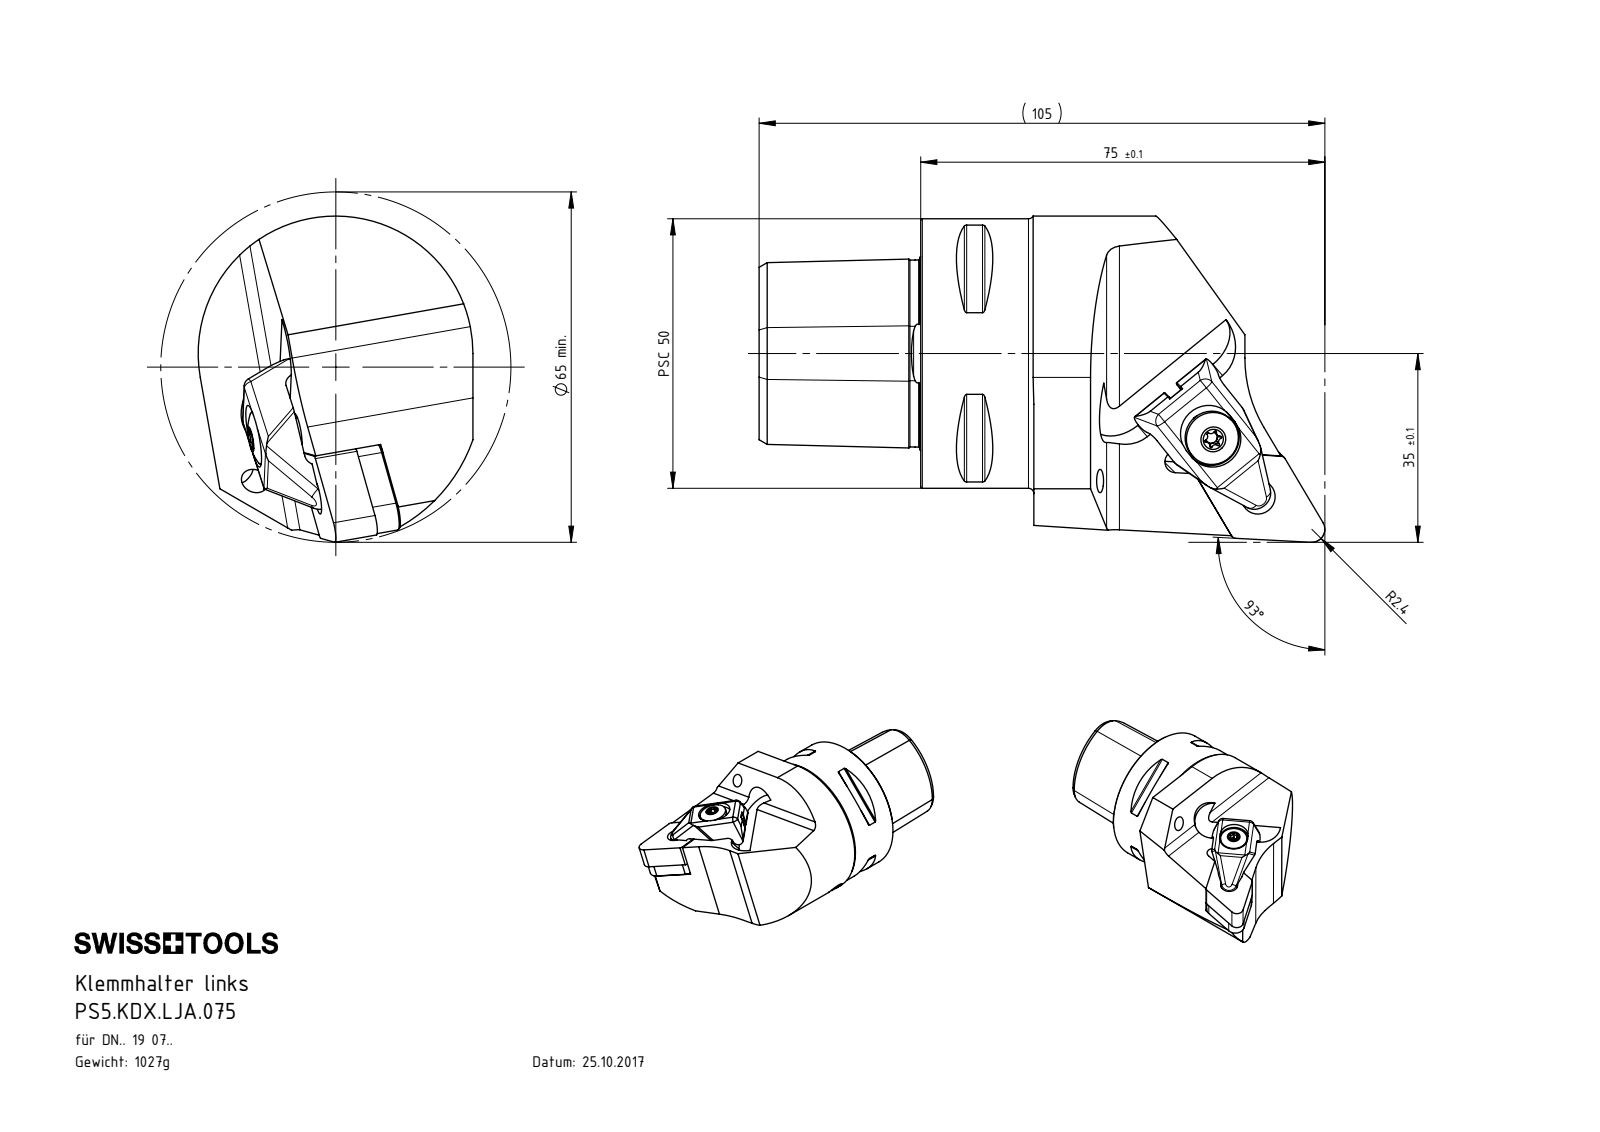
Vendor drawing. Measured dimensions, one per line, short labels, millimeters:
name: DNMG190724; Feder; Bratze komplett; Spannschraube (+6 more)
written by: SolidWorks 2017 (CONFIG_CONTROL_DESIGN)
unit: mm
bodies: 9 solids, 410 faces (106 planar, 145 cylindrical, 159 other)
size: 105.07 × 60.57 × 51
volume: 129 904 mm³; area: 27 478 mm²
holes: 3× ⌀5, 2× ⌀4.2, 1× ⌀4, 1× ⌀5.75, 1× ⌀6, 1× ⌀6.1, 1× ⌀6.35, 1× ⌀8.15, 1× ⌀8.5, 1× ⌀9.3, 1× ⌀14.5, 1× ⌀21
bosses: 2× ⌀6, 2× ⌀5, 1× ⌀50, 1× ⌀9.8, 1× ⌀7, 1× ⌀6.5, 1× ⌀5.8
rounds: 11× R0.2, 10× R1.6, 8× R0.5, 6× R0.39, 6× R0.72, 4× R3.3, 3× R0.69, 3× R0.69
face distances: 7.64, 15.48, 30, 15.46, 51, 21, 7.94, 4.79, 12.43, 12.73
hole spacings: 0.4, 15.91, 16.02, 16.1, 16.31, 16.41, 16.49, 26
